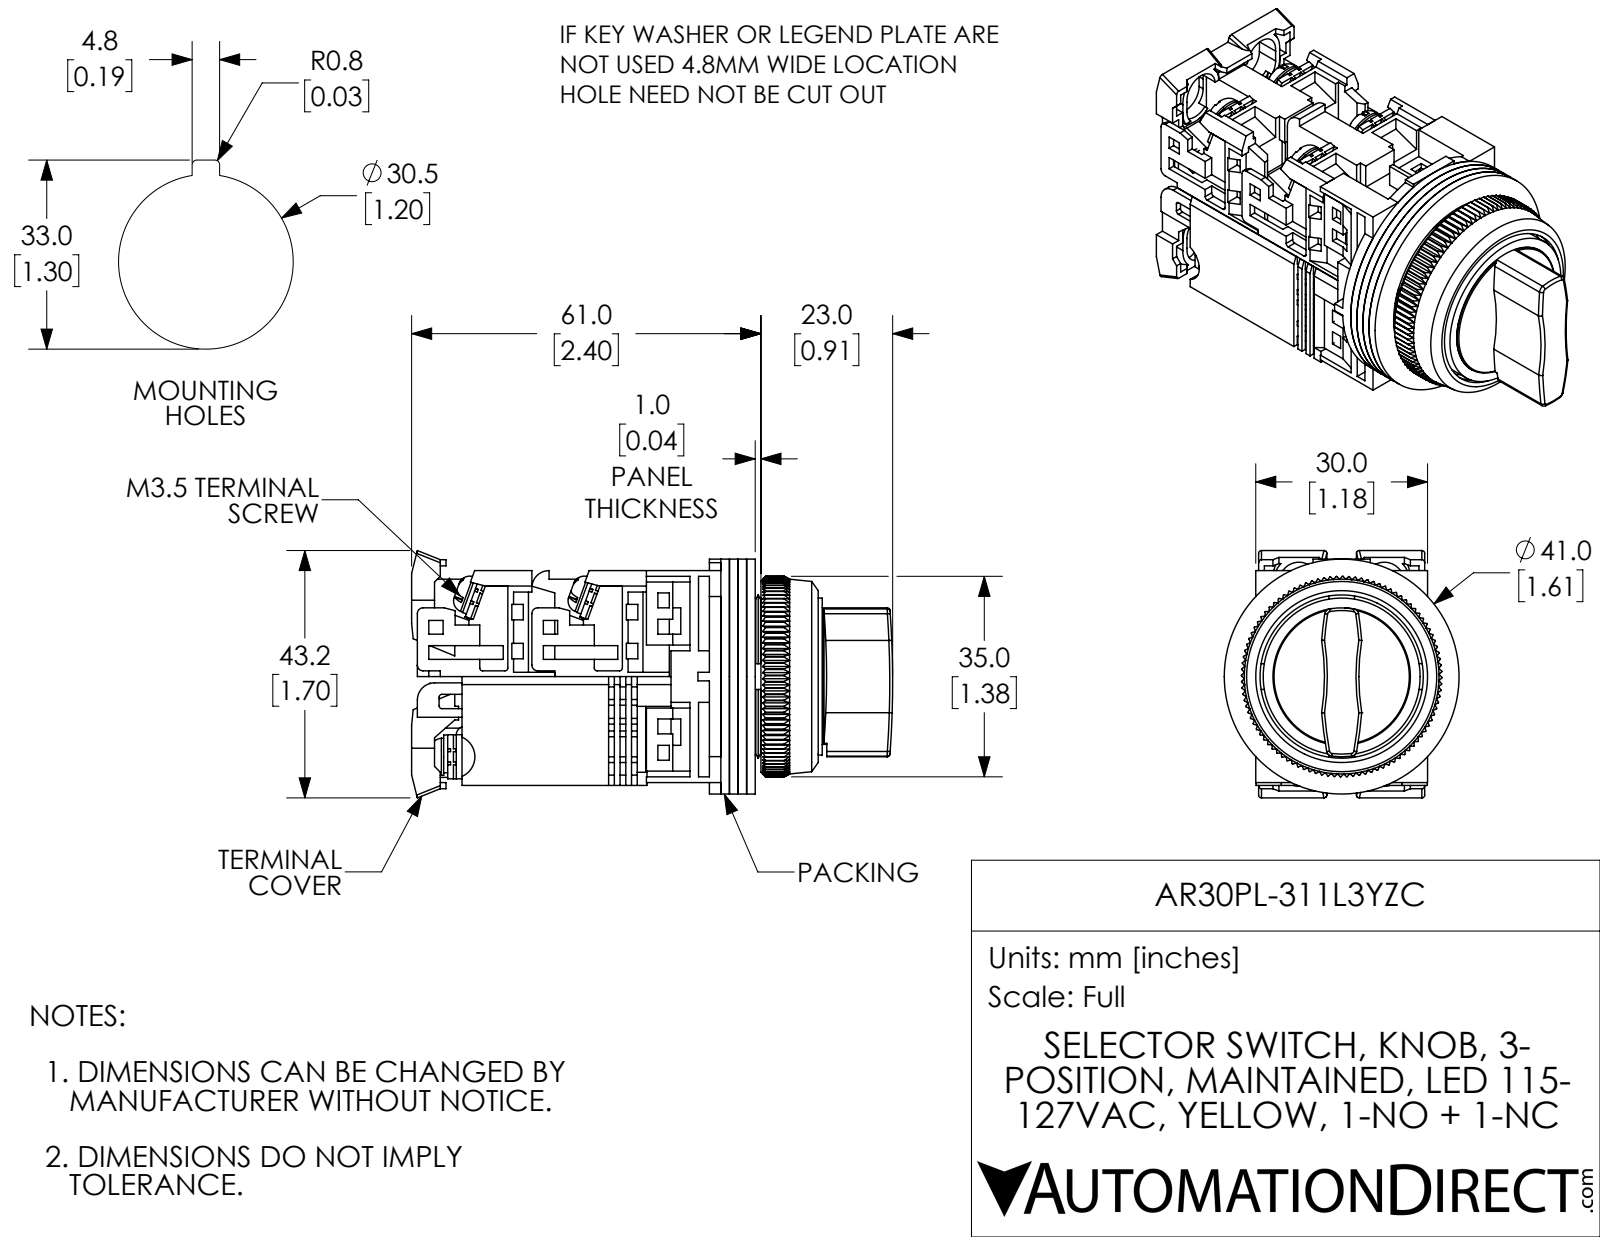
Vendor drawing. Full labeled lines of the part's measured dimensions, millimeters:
Part name (STEP PRODUCT): AR30PL-311L3YZC
STEP written by: SolidWorks 2017 (AUTOMOTIVE_DESIGN)
Units: millimetres
Bodies: 34 solids, 2724 faces (2033 planar, 354 cylindrical, 337 other)
Overall size (bounding box): 84 × 43.2 × 41
Volume: 56 400 mm³ · Surface area: 45 630 mm²
Round holes (diameter × count): ⌀3.5 ×8, ⌀3.6 ×6, ⌀3 ×3, ⌀12 ×1, ⌀18 ×1, ⌀19.5 ×1, ⌀21 ×1, ⌀28.5 ×1, ⌀30 ×1, ⌀31.8 ×1
Round bosses / shafts (diameter × count): ⌀6.6 ×6, ⌀3.5 ×4, ⌀1.6 ×2, ⌀41 ×1, ⌀29.2 ×1, ⌀27.4 ×1, ⌀24 ×1, ⌀22.5 ×1
Partial cylindrical surfaces — rounded edges, fillets, slot ends (radius × count): R1.5 ×25, R0.5 ×15, R1 ×8, R3.5 ×4, R4.5 ×4, R3 ×3, R40 ×2, R75 ×2
Main face-to-face distances: 1.5, 3, 4.5, 1, 19, 2, 20, 1.6, 17.5, 5
Hole centre spacings: 14.7, 6.8, 16.2, 7.5, 15.8, 0.5, 7.7, 14.8
